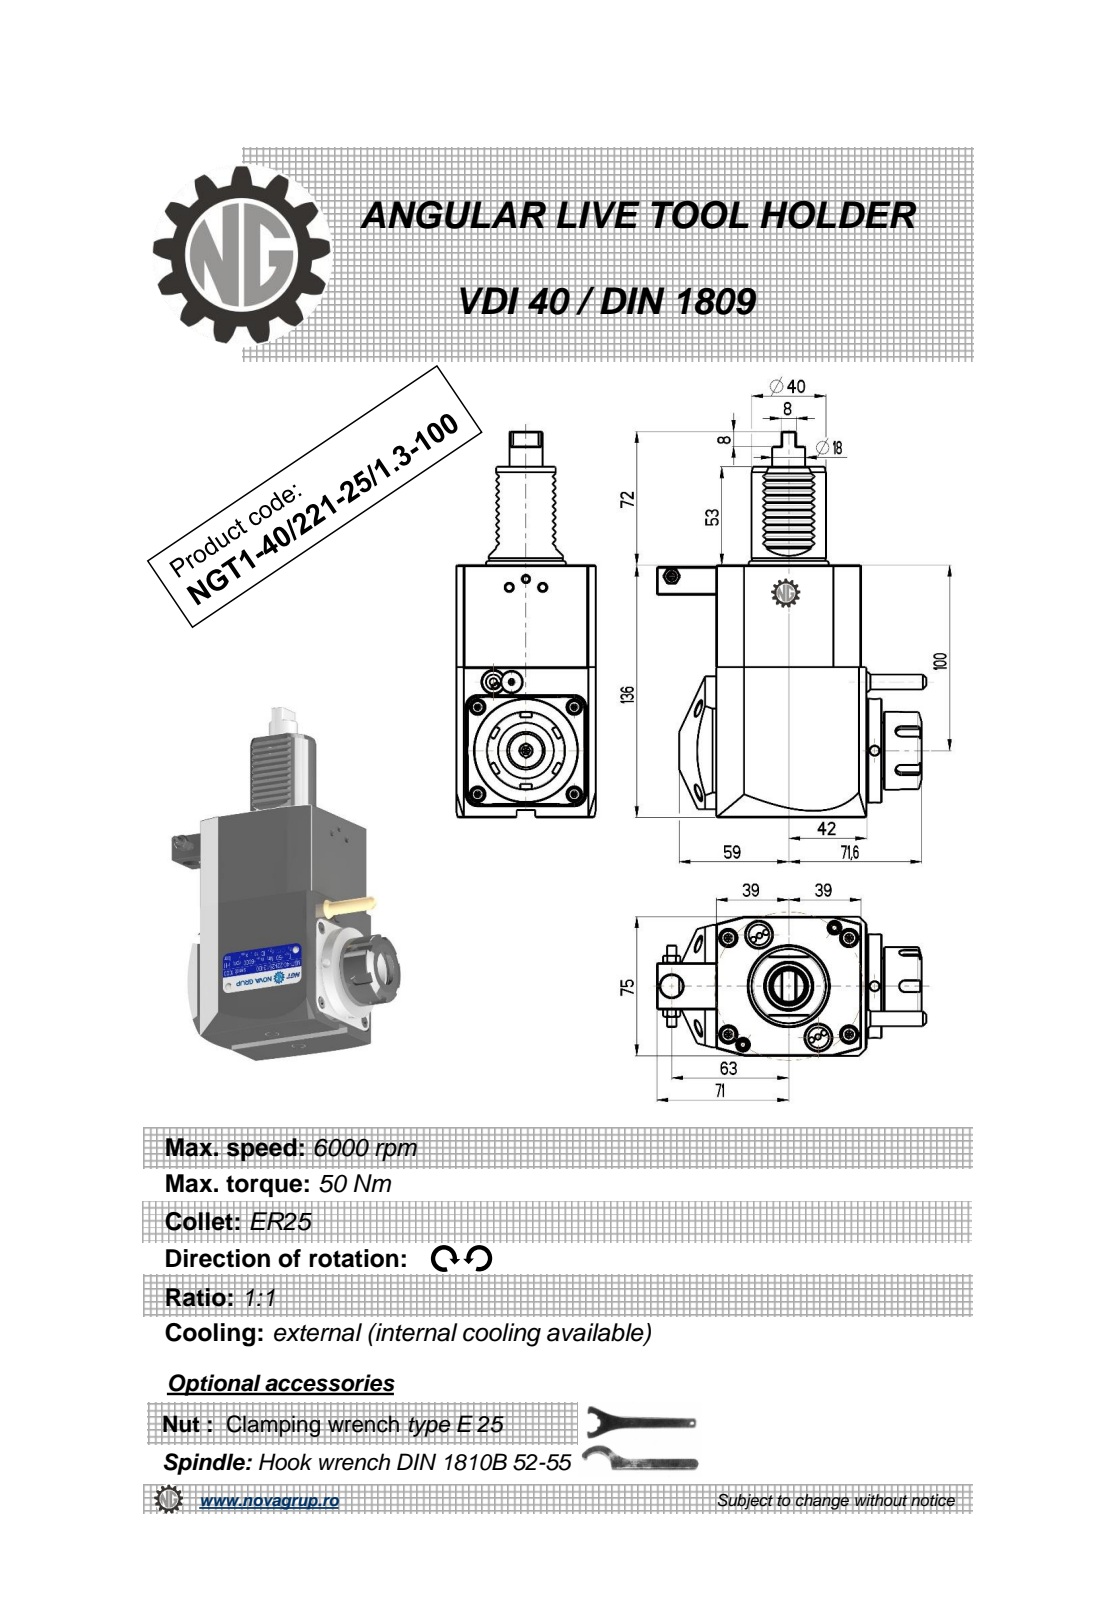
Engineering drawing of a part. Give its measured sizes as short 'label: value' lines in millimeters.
name: NGT1_40_221_25_1_3_100
written by: PRO/ENGINEER BY PARAMETRIC TECHNOLOGY CORPORATION, 2010280 (CONFIG_CONTROL_DESIGN)
unit: mm
bodies: 1 solid, 467 faces (224 planar, 94 cylindrical, 149 other)
size: 208 × 145.14 × 75
volume: 969 504 mm³; area: 75 952 mm²
holes: 3× ⌀5, 1× ⌀3, 1× ⌀4.2, 1× ⌀9.5, 1× ⌀12, 1× ⌀20.3
bosses: 1× ⌀56, 1× ⌀43, 1× ⌀42, 1× ⌀40, 1× ⌀33, 1× ⌀17.8, 1× ⌀11.2, 1× ⌀8.96
rounds: 20× R0.3, 12× R0.26, 6× R0.22, 5× R3, 2× R0.8, 1× R40
face distances: 75, 136, 78, 81, 3, 11, 8, 84.88, 8.2, 80.8
hole spacings: 40.93, 58.19, 92.5, 109.25, 144.12
